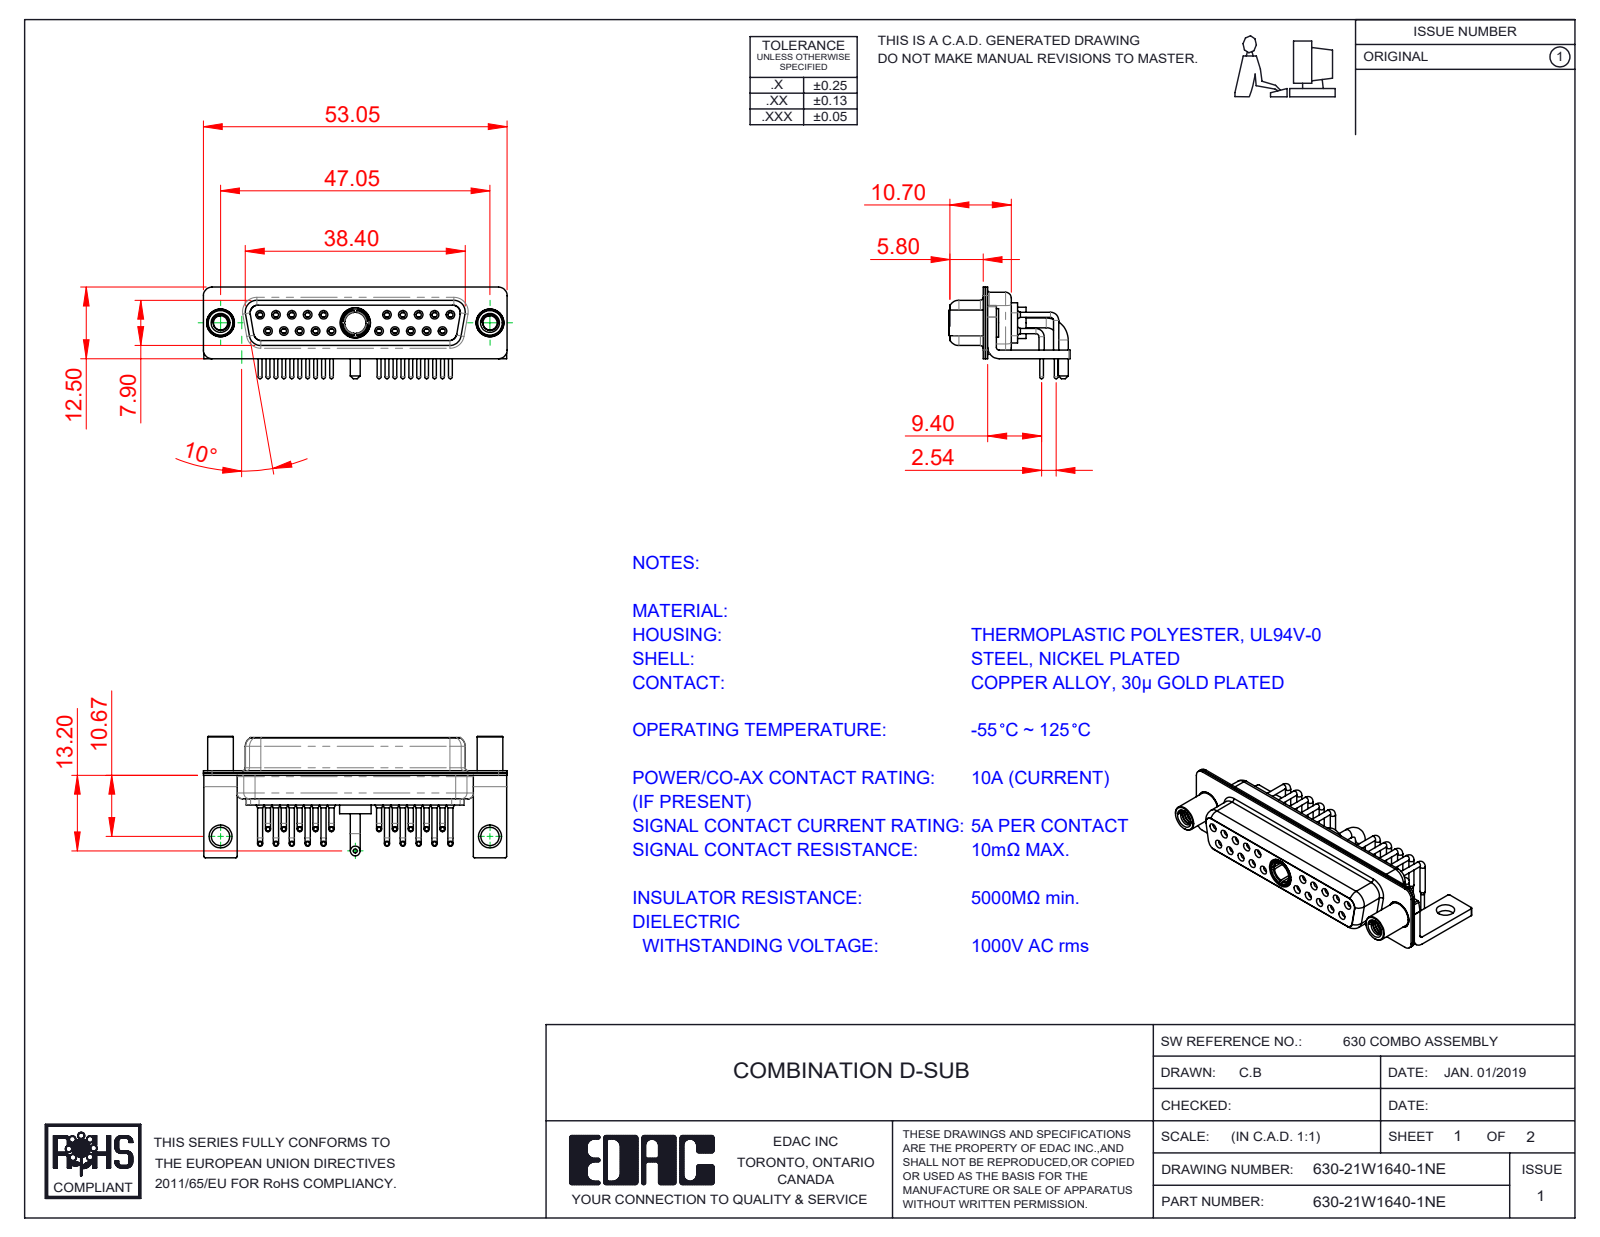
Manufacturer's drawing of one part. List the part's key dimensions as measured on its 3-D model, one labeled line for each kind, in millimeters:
Part name (STEP PRODUCT): 630Combo Stabilizer Bracket; Power Socket_10A RA; 630-21W1640-1NE; 630Combo Shell Rear_25 Contacts (+5 more)
STEP written by: SolidWorks 2020 (CONFIG_CONTROL_DESIGN)
Units: millimetres
Bodies: 29 solids, 1515 faces (418 planar, 694 cylindrical, 403 other)
Overall size (bounding box): 53.05 × 21.2 × 16
Volume: 4 352 mm³ · Surface area: 10 224 mm²
Round holes (diameter × count): ⌀0.9 ×20, ⌀1.1 ×20, ⌀1.5 ×20, ⌀2 ×20, ⌀1.6 ×10, ⌀1.7 ×10, ⌀4.85 ×3, ⌀2.5 ×2, ⌀3.2 ×2, ⌀4 ×2, ⌀4.05 ×2, ⌀3.7 ×1
Round bosses / shafts (diameter × count): ⌀0.9 ×20, ⌀0.65 ×20, ⌀1.6 ×10, ⌀5 ×2, ⌀4.95 ×2, ⌀4.8 ×2, ⌀4.5 ×2, ⌀1.7 ×2
Partial cylindrical surfaces — rounded edges, fillets, slot ends (radius × count): R0.25 ×16, R1.5 ×16, R2 ×13, R1.35 ×8, R1.6 ×8, R0.5 ×5, R0.6 ×4, R0.65 ×4
Main face-to-face distances: 0.4, 0.45, 1.4, 8.45, 0.8, 1.8, 8.9, 6.2, 7.05, 1.5
Hole centre spacings: 3.16, 2.77, 5.54, 8.31, 5.04, 19.39, 20.97, 22.16
